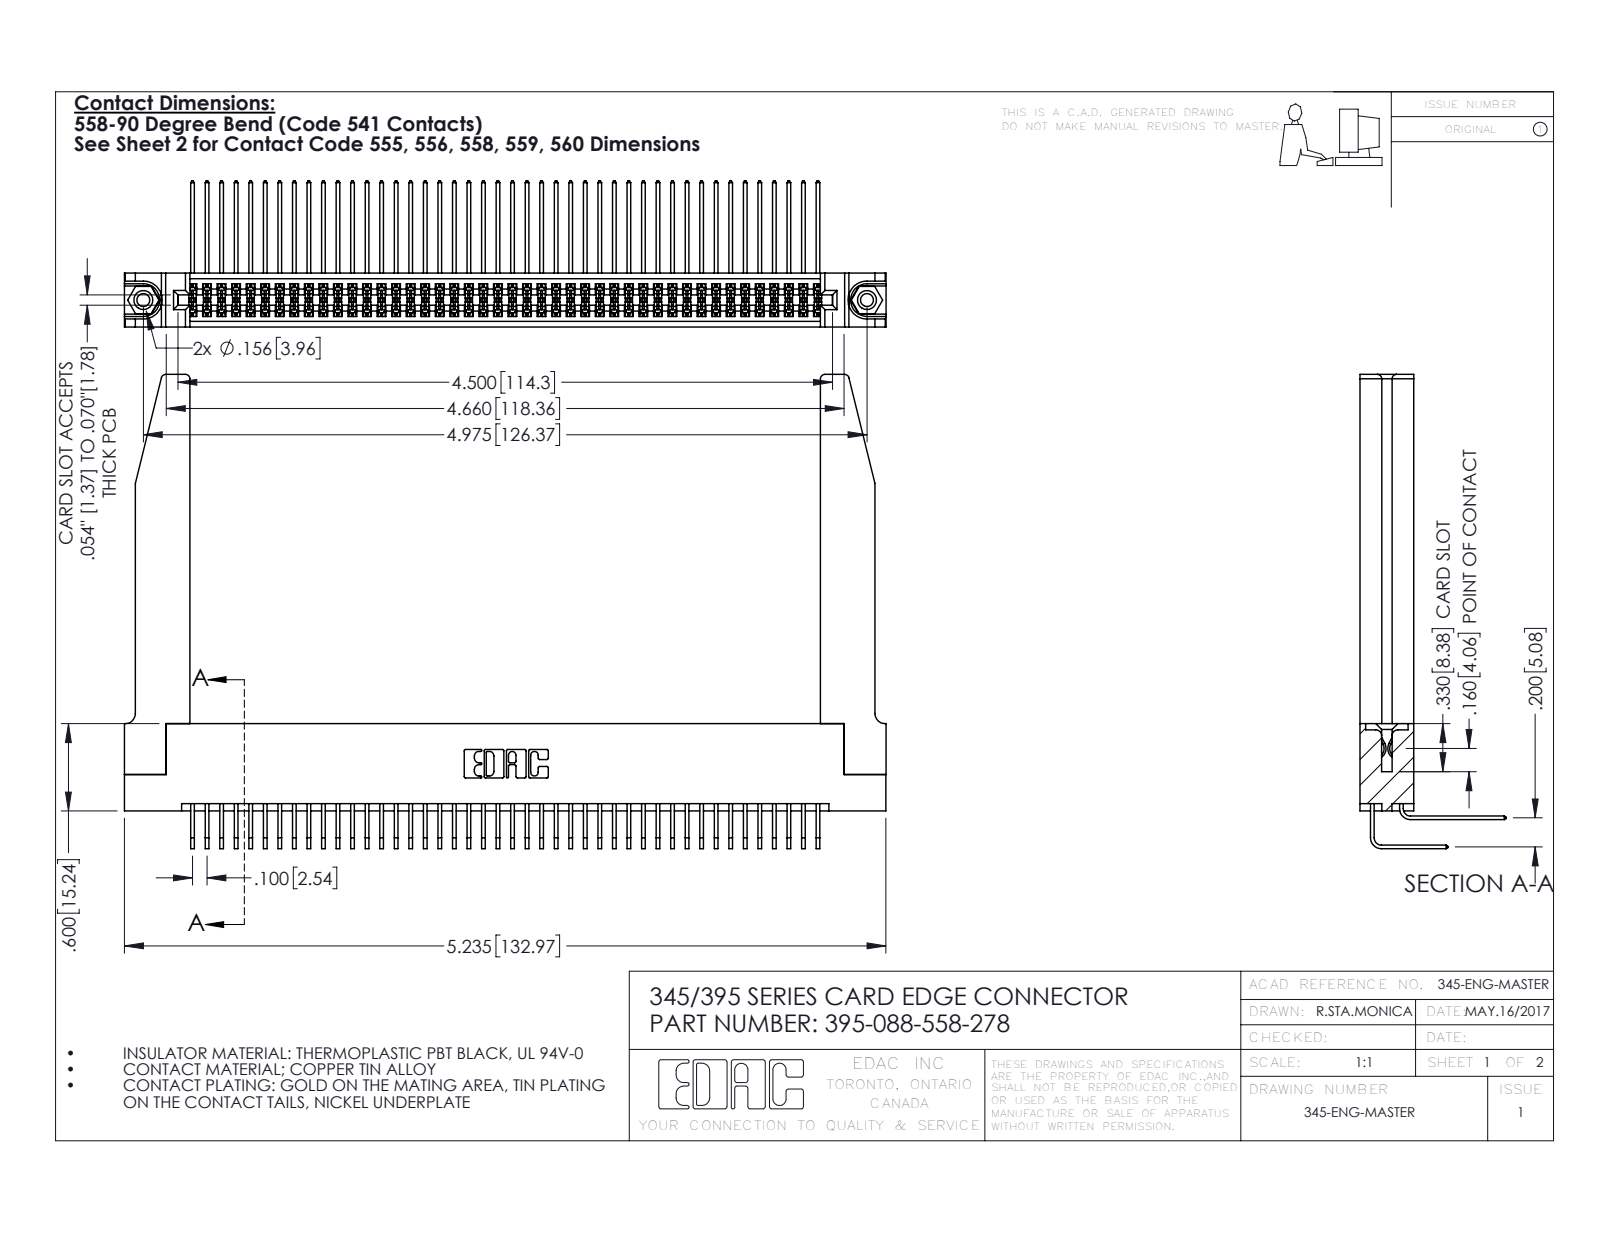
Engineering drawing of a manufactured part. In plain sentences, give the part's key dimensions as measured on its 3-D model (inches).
The part is named "345-292-001_558 Tail - 2; 345-220-078_345-220-078; 345-250-001_345-250-001-102; 395-088-558-278 (+2 more)". Its 3-D file was written by "SolidWorks 2016 (CONFIG_CONTROL_DESIGN)". It is 93 solids with 4936 faces: 3302 planar, 1582 cylindrical and 52 other. Overall it measures 5.236 by 3.259 by 1.005 inches. Its volume is 1.295 cubic inches and its surface area 45.17 square inches. Round holes: 2 of diameter 0.089, 2 of diameter 0.125, 2 of diameter 0.156, 1 of diameter 0.064. Round bosses or shafts: 2 of diameter 0.155. Partial cylindrical surfaces (rounded edges, fillets, slot ends): 133 of radius 0.006, 22 of radius 0.01, 8 of radius 0.03, 6 of radius 0.007, 6 of radius 0.031, 3 of radius 0.026, 2 of radius 0.014, 2 of radius 0.019. The main face-to-face distances are 0.072, 0.37, 0.298, 0.2, 0.098, 0.272, 0.025, 0.225, 0.285, 0.025. The hole center spacings are 0.27, 4.739, 4.975.
